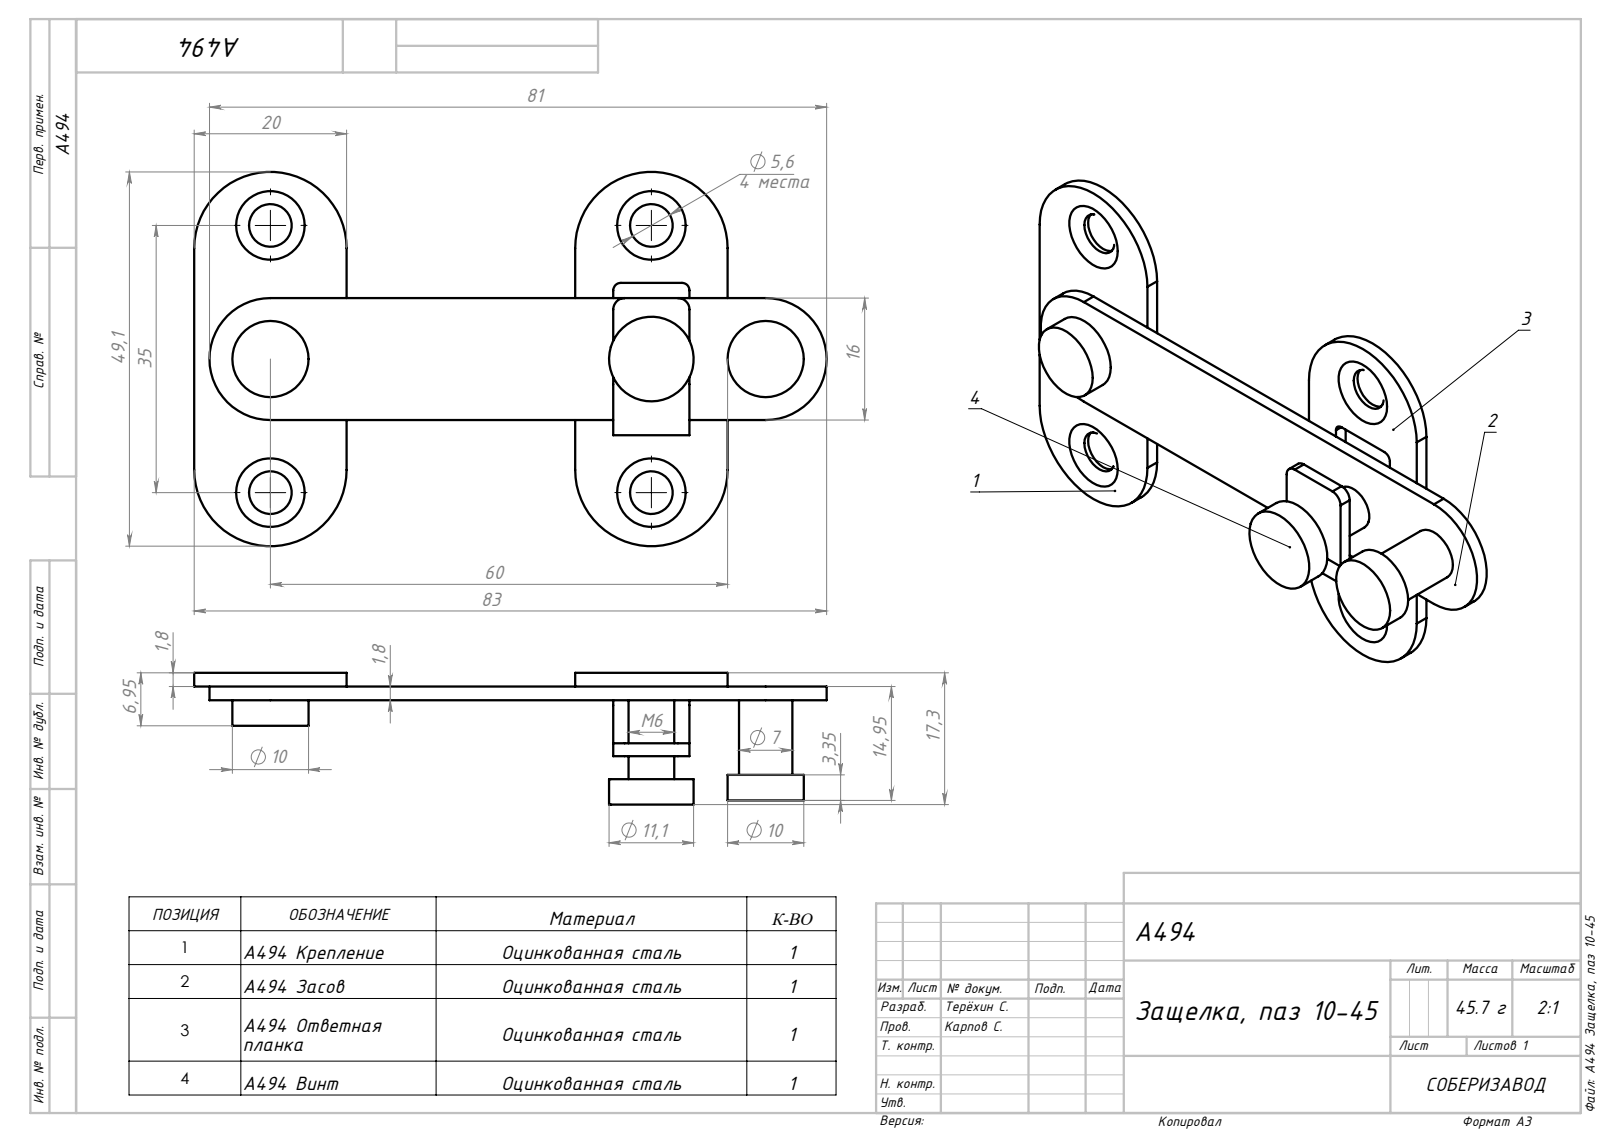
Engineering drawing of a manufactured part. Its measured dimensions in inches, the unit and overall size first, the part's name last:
Units: inches
Overall size (bounding box): 3.268 × 1.933 × 0.681
Round holes (diameter × count): ⌀0.22 ×4, ⌀0.197 ×1, ⌀0.256 ×1
Round bosses / shafts (diameter × count): ⌀0.394 ×2, ⌀0.437 ×1, ⌀0.276 ×1, ⌀0.236 ×1
Partial cylindrical surfaces — rounded edges, fillets, slot ends (radius × count): R0.059 ×5, R0.039 ×4, R0.394 ×4, R0.315 ×2, R0.197 ×1, R0.264 ×1
Main face-to-face distances: 0.071, 0.142, 0.132, 0.591, 0.407, 0.394, 0.787, 0.386, 0.022, 0.63
Hole centre spacings: 0.69, 1.368, 1.181, 1.38, 1.816
Volume: 0.413 in³ · Surface area: 12.52 in²
Bodies: 4 solids, 83 faces (33 planar, 42 cylindrical, 8 other)
Part name (STEP PRODUCT): A494 Крепление_00; A494 Винт_00; A494 Засов_00; A494 Защелка, паз 10-45 (+1 more)
STEP written by: SolidWorks 2022 (AUTOMOTIVE_DESIGN)
